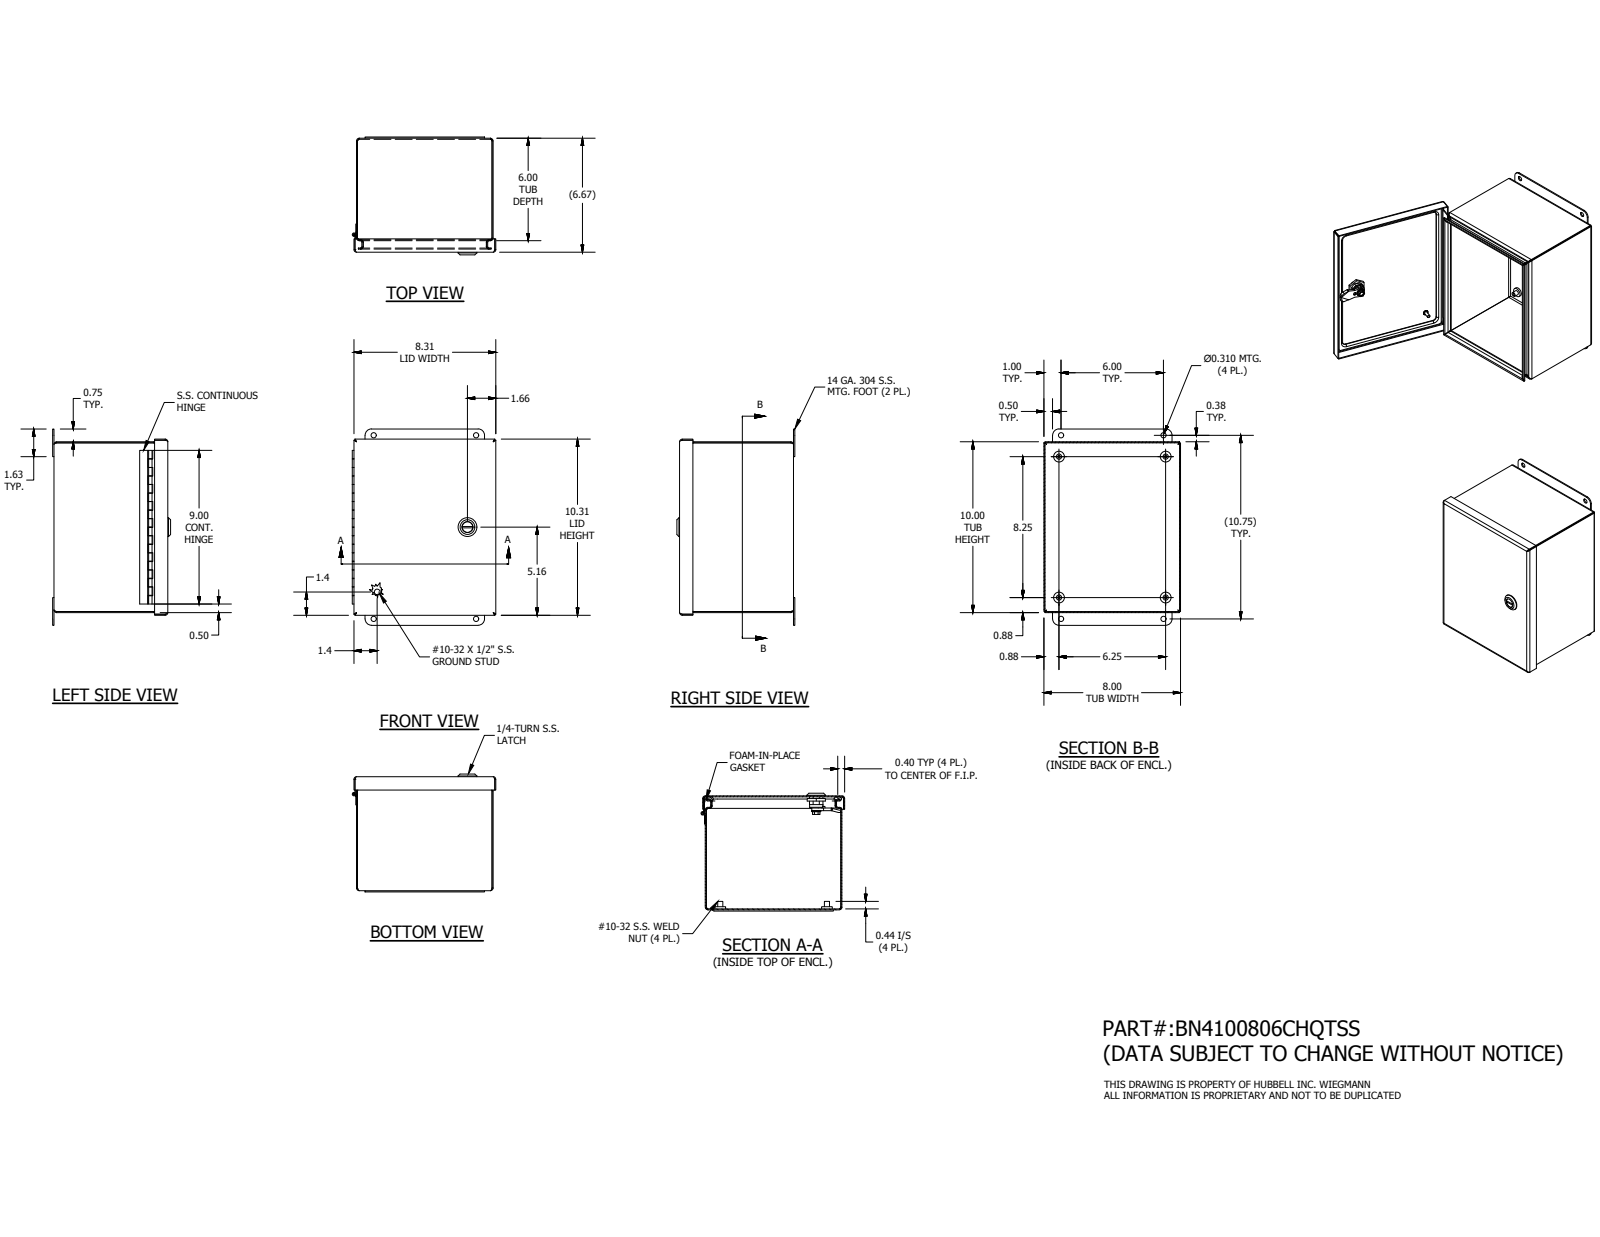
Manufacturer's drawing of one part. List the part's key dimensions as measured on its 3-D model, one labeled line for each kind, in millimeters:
Part name (STEP PRODUCT): BN41008CHQTSSLID; 10x8; 34854; H4050549LH (+8 more)
STEP written by: Autodesk Inventor 2016 (AUTOMOTIVE_DESIGN)
Units: millimetres
Bodies: 19 solids, 608 faces (323 planar, 191 cylindrical, 94 other)
Overall size (bounding box): 292.1 × 213.66 × 175.39
Volume: 518 770 mm³ · Surface area: 647 983 mm²
Round holes (diameter × count): ⌀3.96 ×4, ⌀7.87 ×4, ⌀2.96 ×1, ⌀5 ×1, ⌀8 ×1, ⌀10 ×1, ⌀10.2 ×1, ⌀16.1 ×1
Round bosses / shafts (diameter × count): ⌀15.88 ×4, ⌀7.62 ×4, ⌀28 ×1, ⌀19.8 ×1, ⌀16 ×1, ⌀15.2 ×1, ⌀13.5 ×1, ⌀12.8 ×1
Partial cylindrical surfaces — rounded edges, fillets, slot ends (radius × count): R2.38 ×20, R3.88 ×20, R3.17 ×16, R0.5 ×8, R4 ×4, R9.53 ×4, R2.31 ×2, R6.45 ×1
Main face-to-face distances: 1.5, 1.49, 252.5, 167.99, 169.48, 166.49, 167.98, 201.71, 203.2, 200.21
Hole centre spacings: 31.91, 241.32, 152.4, 158.75, 158.78, 158.79, 177.17, 209.55
